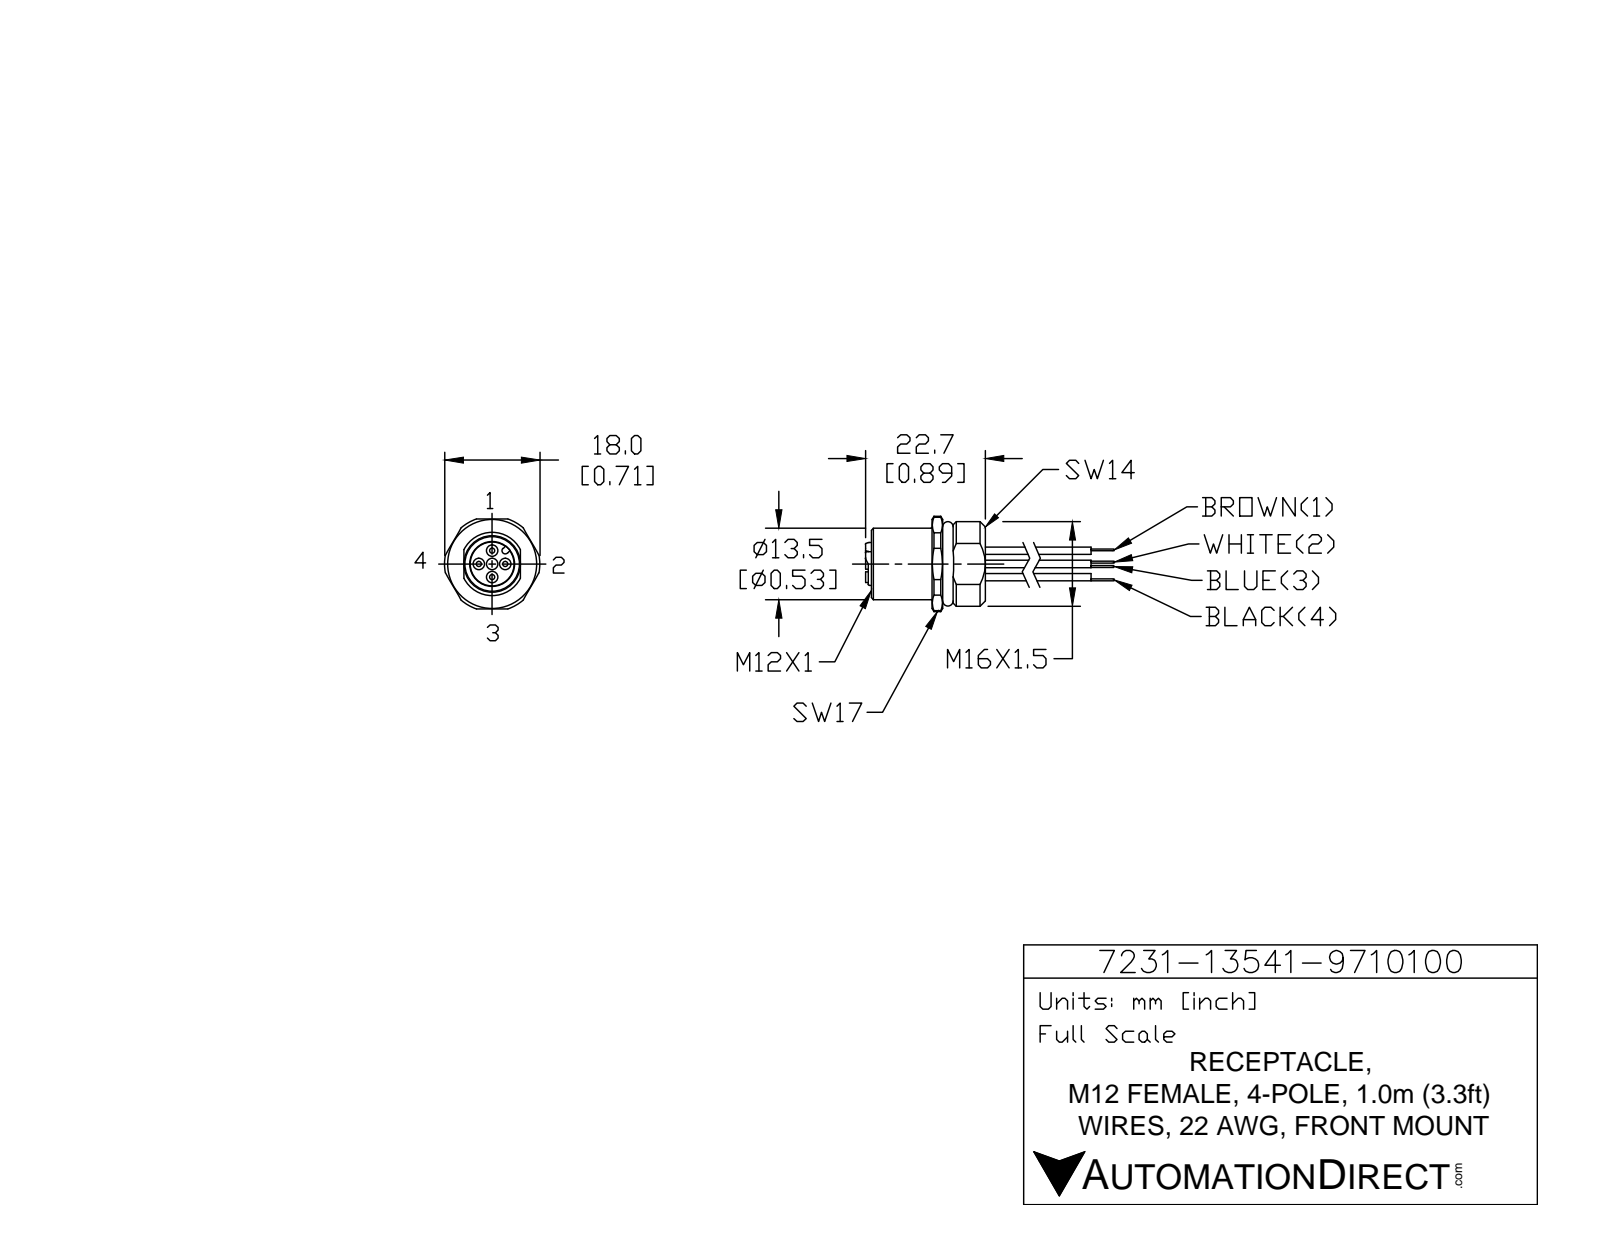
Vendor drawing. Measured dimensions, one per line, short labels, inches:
name: 7231-13541-9710100
written by: SolidWorks 2018 (AUTOMOTIVE_DESIGN)
unit: in
bodies: 1 solid, 153 faces (38 planar, 63 cylindrical, 52 other)
size: 1.677 × 0.709 × 0.669
volume: 0.204 in³; area: 3.825 in²
holes: 5× ⌀0.043, 1× ⌀0.43, 1× ⌀0.48, 1× ⌀0.512
bosses: 5× ⌀0.079, 4× ⌀0.055, 1× ⌀0.531, 1× ⌀0.319
rounds: 6× R0.008, 1× R0.024, 1× R0.315, 1× R0.354
face distances: 0.276, 0.555, 0.354, 0.079, 0.28, 0.201, 0.551, 0.831, 0.039, 0.669
hole spacings: 0.098, 0.139, 0.197, 0.098, 0.099
